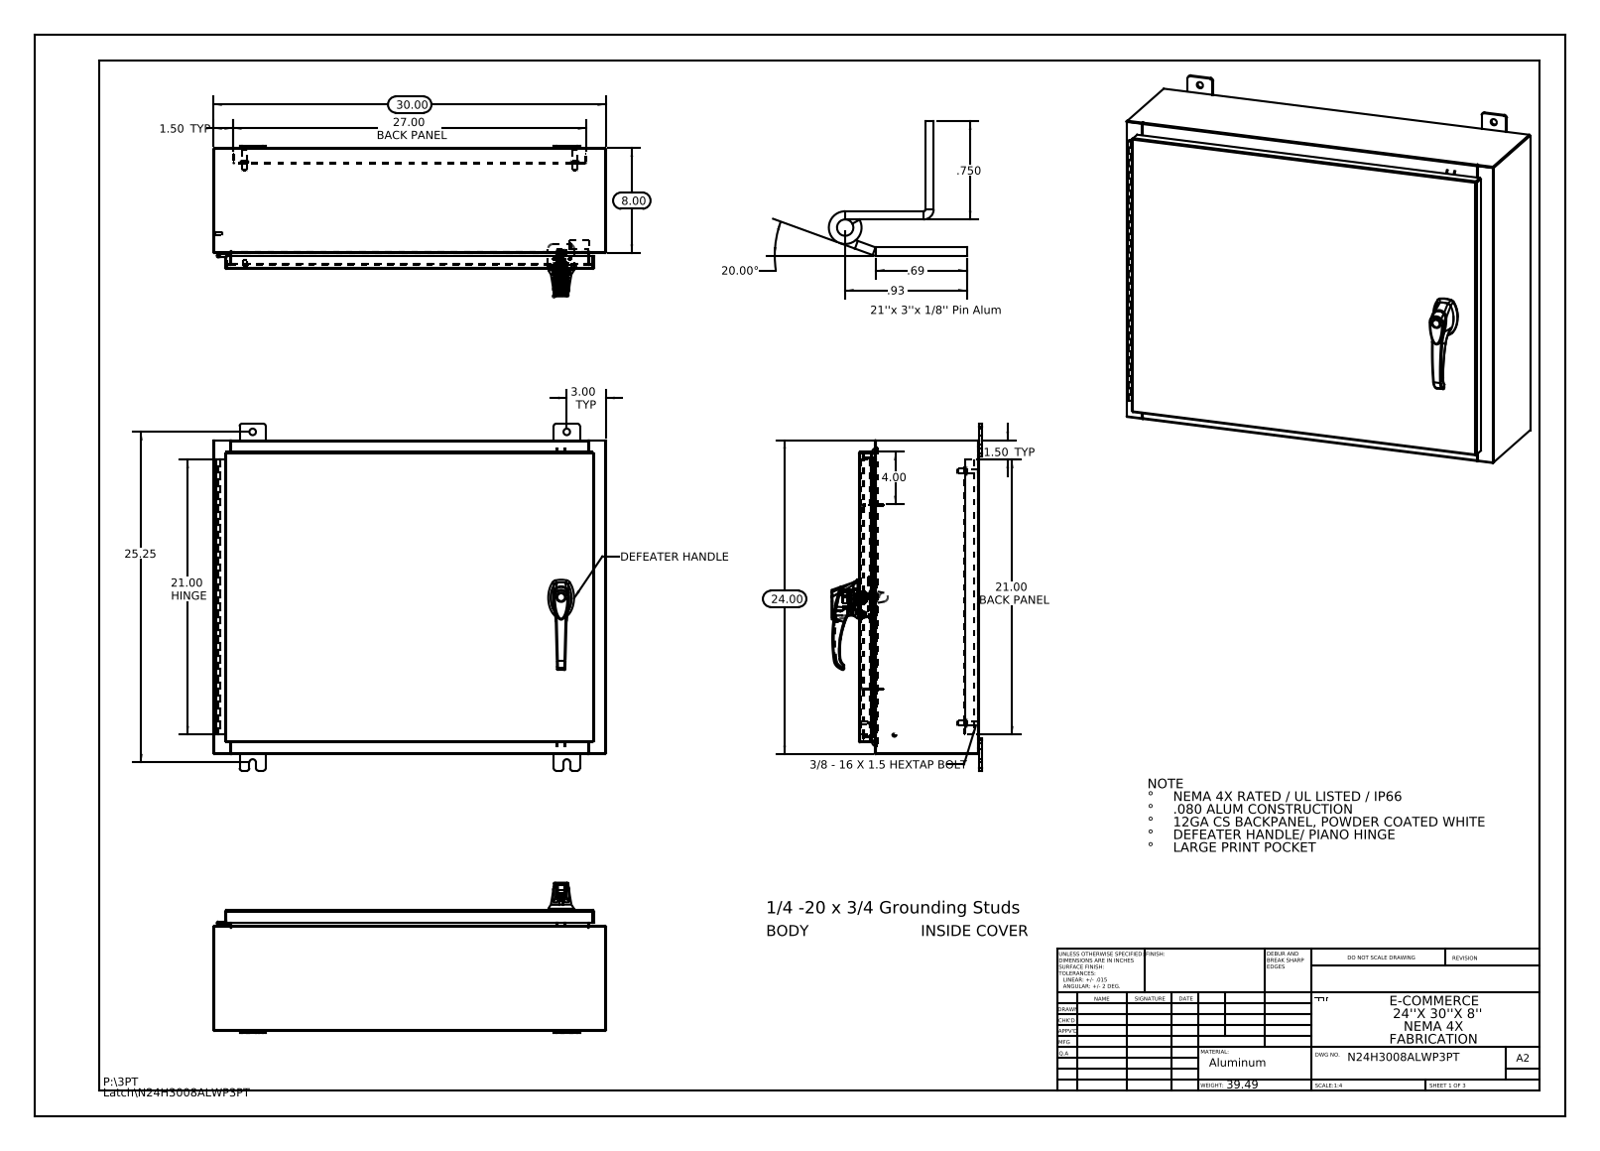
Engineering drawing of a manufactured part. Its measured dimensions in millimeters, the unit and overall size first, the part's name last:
Units: millimetres
Overall size (bounding box): 762 × 673.1 × 292
Round holes (diameter × count): ⌀12.7 ×8, ⌀6.4 ×4, ⌀3.5 ×3, ⌀4.1 ×3, ⌀2 ×2, ⌀5.2 ×2, ⌀8 ×2, ⌀11.1 ×2, ⌀3.2 ×1, ⌀3.2 ×1, ⌀5 ×1, ⌀7 ×1
Round bosses / shafts (diameter × count): ⌀15.9 ×4, ⌀9.5 ×4, ⌀8.4 ×4, ⌀4 ×4, ⌀3.6 ×4, ⌀8 ×3, ⌀6 ×3, ⌀30 ×1
Partial cylindrical surfaces — rounded edges, fillets, slot ends (radius × count): R3 ×37, R0.2 ×33, R4.8 ×24, R0.3 ×22, R2.2 ×18, R1 ×15, R0.7 ×12, R0.2 ×6
Main face-to-face distances: 1.9, 231.8, 229.9, 233.7, 2.6, 25.4, 27.3, 204.5, 206.4, 29.9
Hole centre spacings: 195.1, 609.6, 7.5, 15.9, 21.4, 31.8, 33.4, 39.6
Volume: 4 377 000 mm³ · Surface area: 4 257 000 mm²
Bodies: 37 solids, 2498 faces (883 planar, 917 cylindrical, 698 other)
Part name (STEP PRODUCT): N24H3008ALWP3PT; N24H3008ALWP3PT Body; 00005310_26163101; g26103103_26163303 (+8 more)
STEP written by: SolidWorks 2013 (CONFIG_CONTROL_DESIGN)
